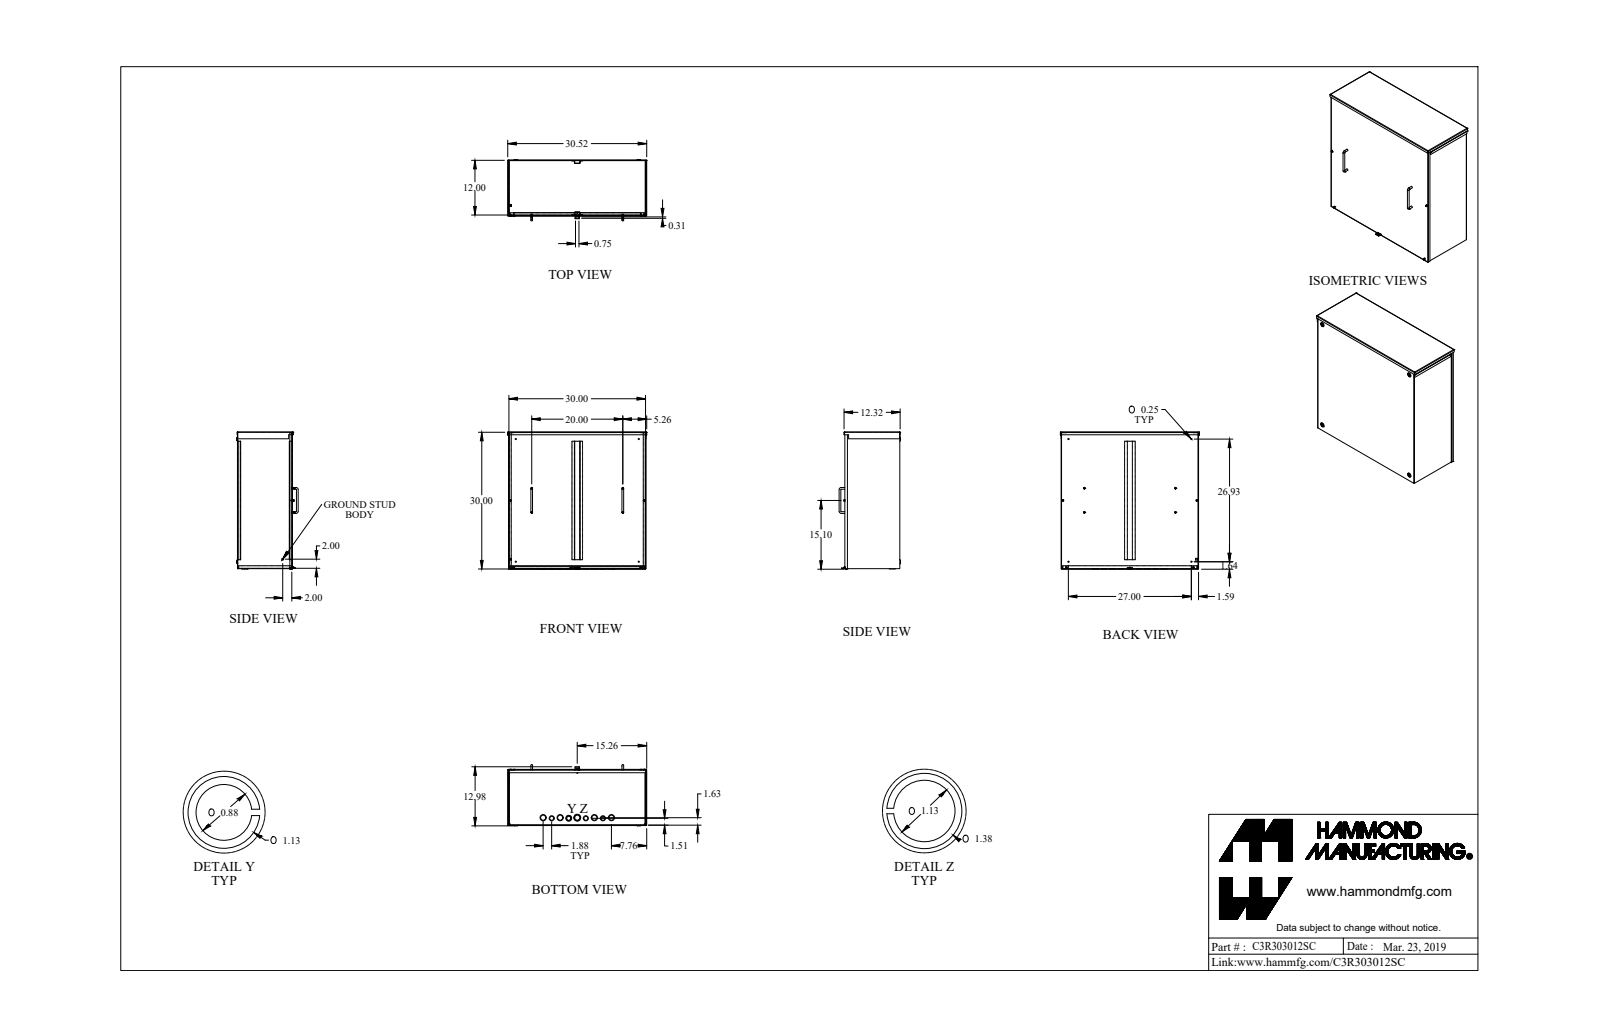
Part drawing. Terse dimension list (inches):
name: C3R303012SC_Default
written by: SolidWorks 2019 (CONFIG_CONTROL_DESIGN)
unit: in
bodies: 19 solids, 653 faces (342 planar, 193 cylindrical, 118 other)
size: 30.519 × 30.135 × 13.478
volume: 261.5 in³; area: 7 281 in²
holes: 5× ⌀0.156, 4× ⌀0.17, 4× ⌀0.203, 4× ⌀0.25, 3× ⌀1.125, 2× ⌀0.875, 2× ⌀0.875, 2× ⌀1.125, 1× ⌀0.125, 1× ⌀0.137
bosses: 9× ⌀0.375, 8× ⌀0.19, 4× ⌀1.125, 4× ⌀0.367, 3× ⌀1.375, 2× ⌀1.375, 2× ⌀0.375, 1× ⌀0.125
rounds: 28× R0.036, 28× R0.108, 8× R0.109, 8× R0.125, 2× R0.156, 1× R0.029, 1× R0.086
face distances: 0.072, 12, 29.928, 11.928, 12.072, 30, 0.072, 29.856, 29.856, 29.928
hole spacings: 20, 3.75, 0.024, 1.879, 1.88, 5.3, 5.392, 5.627
